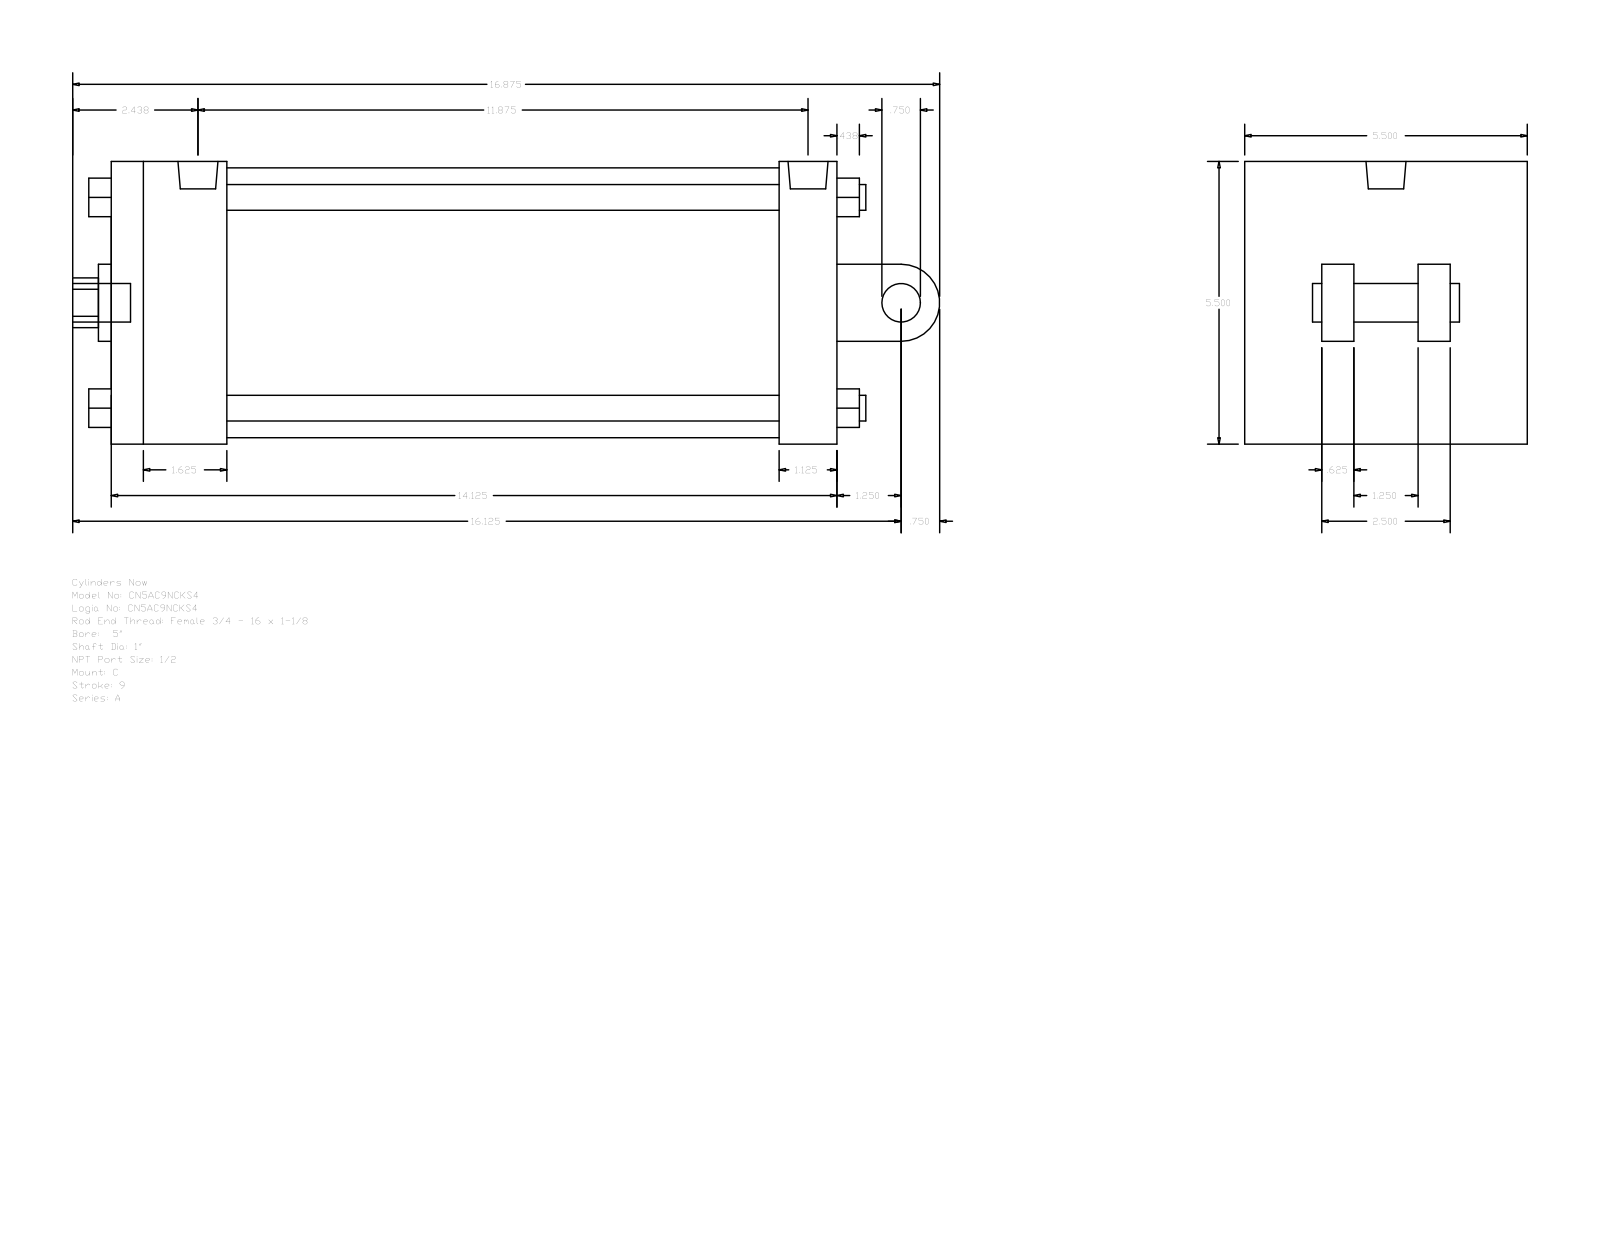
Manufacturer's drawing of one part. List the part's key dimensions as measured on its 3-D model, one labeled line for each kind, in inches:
Part name (STEP PRODUCT): A_C__0500_1
STEP written by: GSSL Pune (CONFIG_CONTROL_DESIGN)
Units: inches
Bodies: 0 solids, 135 faces (102 planar, 33 cylindrical, 0 other)
Overall size (bounding box): 16.875 × 5.5 × 5.5
Round holes (diameter × count): ⌀0.344 ×2, ⌀0.778 ×1, ⌀1 ×1, ⌀1.5 ×1, ⌀5.25 ×1
Round bosses / shafts (diameter × count): ⌀0.5 ×4, ⌀0.75 ×2, ⌀0.344 ×2, ⌀0.778 ×1
Partial cylindrical surfaces — rounded edges, fillets, slot ends (radius × count): R0.484 ×1, R0.75 ×1
Main face-to-face distances: 5.5, 14.125, 1.125, 2.25, 13, 10.75, 11.875, 1.5, 0.625, 1.875
Hole centre spacings: 0.094
